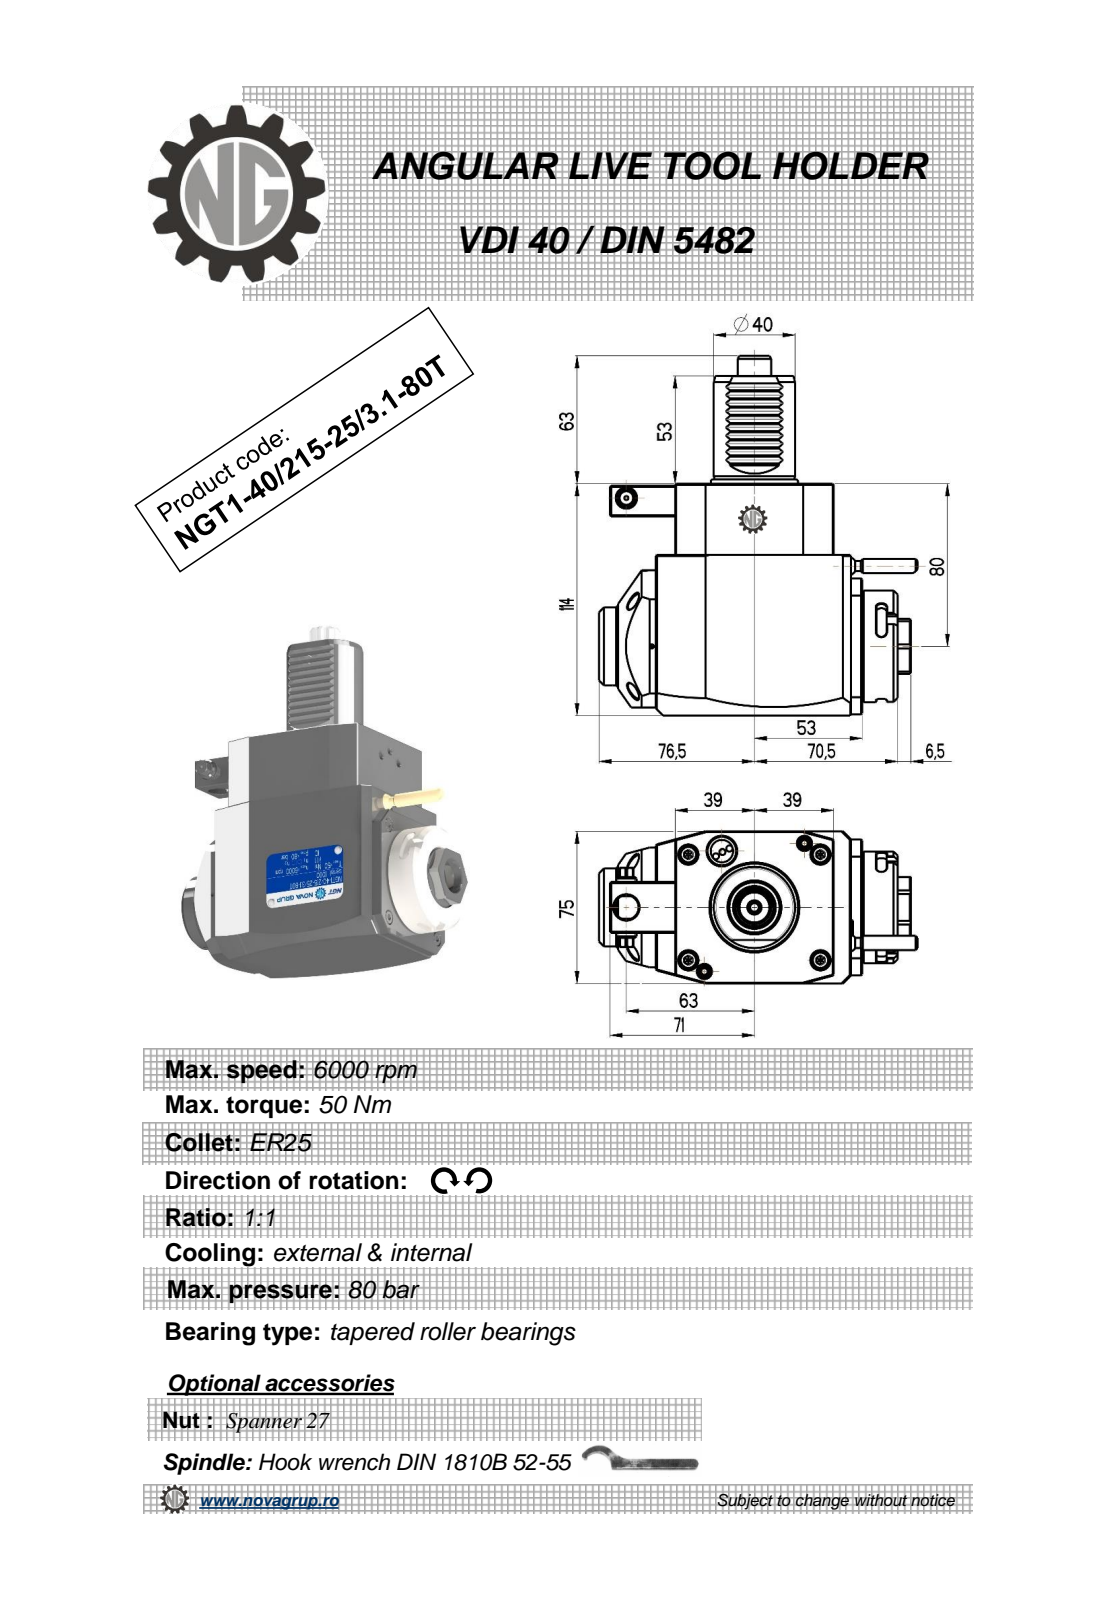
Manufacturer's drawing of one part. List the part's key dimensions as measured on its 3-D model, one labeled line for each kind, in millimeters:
Part name (STEP PRODUCT): NGT1_40_215_25_3_1_80T
STEP written by: PRO/ENGINEER BY PARAMETRIC TECHNOLOGY CORPORATION, 2010280 (CONFIG_CONTROL_DESIGN)
Units: millimetres
Bodies: 1 solid, 401 faces (177 planar, 129 cylindrical, 95 other)
Overall size (bounding box): 177 × 156.83 × 75
Volume: 957 772 mm³ · Surface area: 71 207 mm²
Round holes (diameter × count): ⌀2 ×1, ⌀2.5 ×1, ⌀3 ×1, ⌀4.2 ×1, ⌀4.5 ×1, ⌀5.3 ×1, ⌀9.5 ×1, ⌀12 ×1, ⌀18 ×1
Round bosses / shafts (diameter × count): ⌀8 ×2, ⌀55 ×1, ⌀48 ×1, ⌀40 ×1, ⌀38.5 ×1, ⌀10 ×1, ⌀7 ×1, ⌀5 ×1
Partial cylindrical surfaces — rounded edges, fillets, slot ends (radius × count): R3.03 ×18, R0.3 ×10, R2.5 ×6, R180 ×2, R0.5 ×1, R3.85 ×1, R4.25 ×1, R6.75 ×1
Main face-to-face distances: 75, 114, 14, 17.5, 78, 92, 109.5, 31.5, 35, 79
Hole centre spacings: 37.35, 43.2, 63, 72.5
